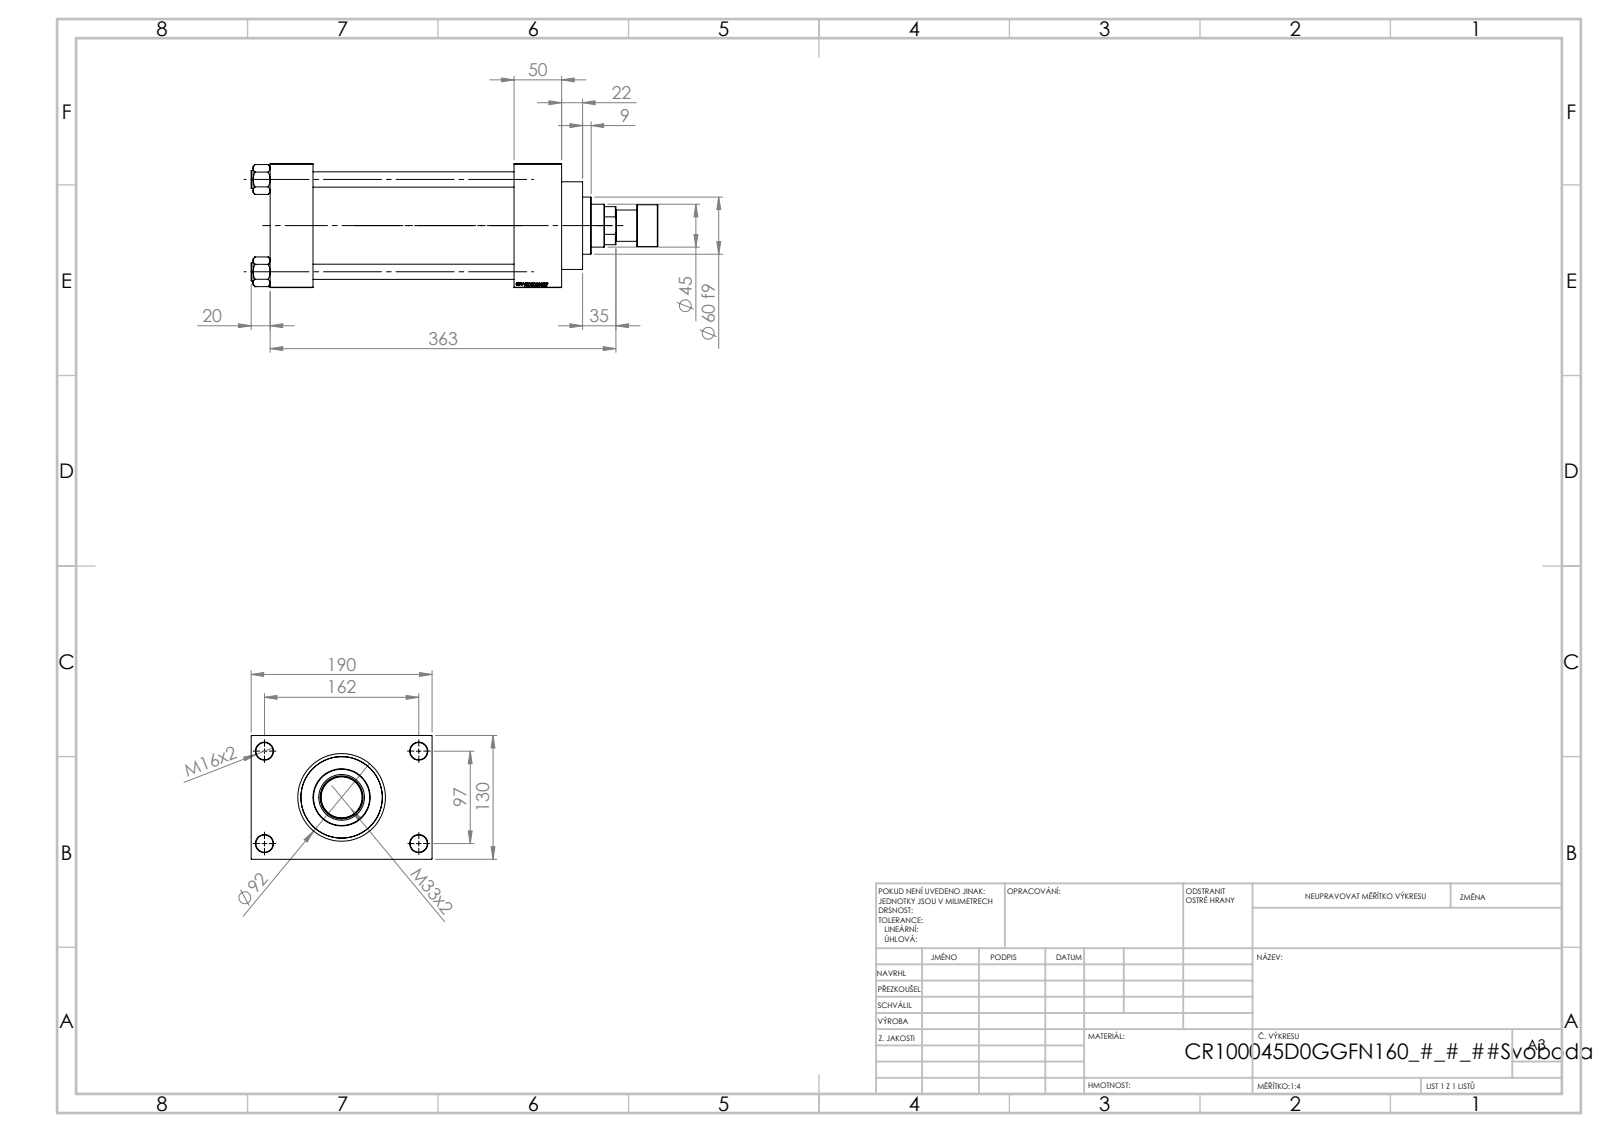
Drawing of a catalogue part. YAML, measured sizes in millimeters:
part_name: "V215_VC_A; V215CR_VCP_D; NUT_M5_D; V215CR_D_TYCINKA (+2 more)"
step_written_by: "SolidWorks 2019 (CONFIG_CONTROL_DESIGN)"
units: millimeters
bodies: {solids: 12, faces: 1165, planar: 548, cylindrical: 93, other: 524}
overall_size: [427, 190, 130]
volume: 3130000
surface_area: 499317
round_holes:
  - {diameter: 16, count: 4}
  - {diameter: 18, count: 4}
  - {diameter: 7, count: 2}
  - {diameter: 26.44, count: 2}
  - {diameter: 35, count: 2}
  - {diameter: 31.5, count: 1}
  - {diameter: 45, count: 1}
  - {diameter: 48, count: 1}
  - {diameter: 76, count: 1}
  - {diameter: 85.5, count: 1}
  - {diameter: 100, count: 1}
round_bosses_or_shafts:
  - {diameter: 19, count: 4}
  - {diameter: 106, count: 1}
  - {diameter: 92, count: 1}
  - {diameter: 60, count: 1}
  - {diameter: 44, count: 1}
  - {diameter: 33, count: 1}
face_to_face_distances: [130, 45, 160, 256, 211, 306, 261, 50, 30, 190]
hole_center_spacings: [32.55, 68.52, 94.41, 96.9, 102.27, 129.45, 161.73, 97]
